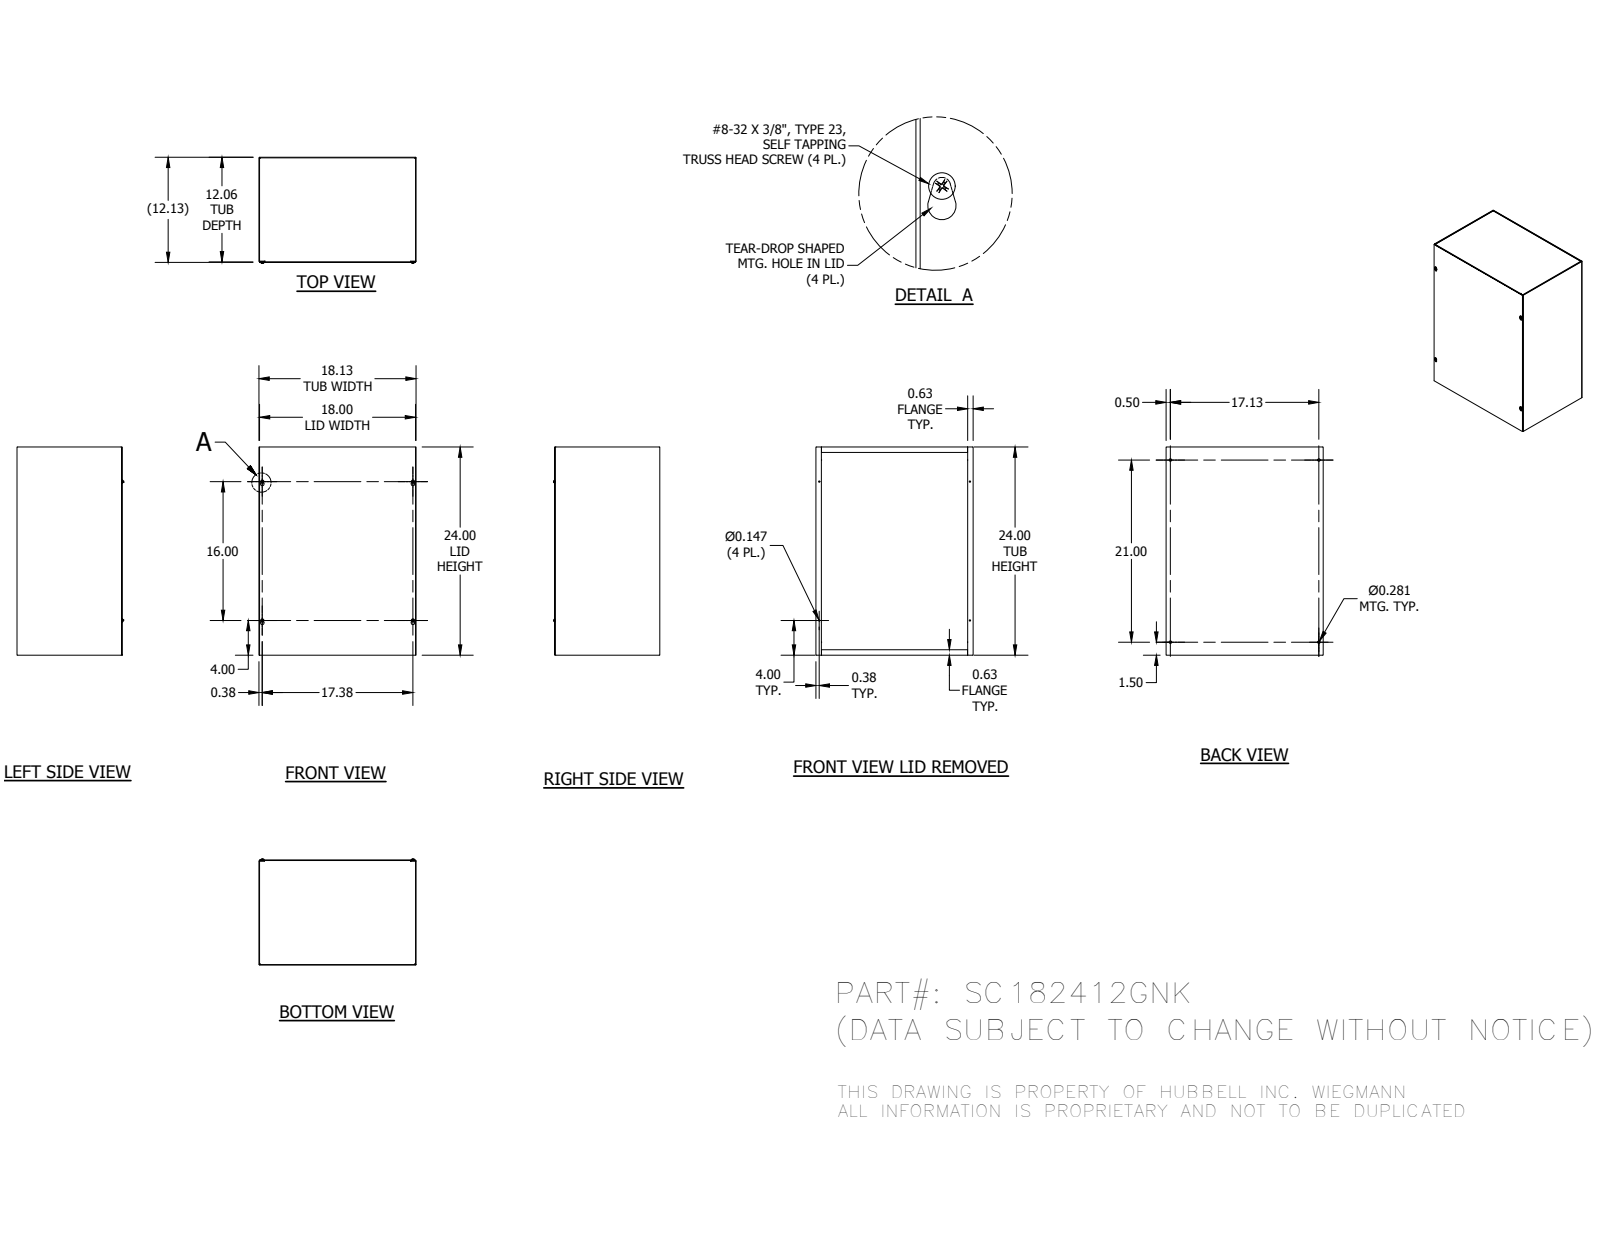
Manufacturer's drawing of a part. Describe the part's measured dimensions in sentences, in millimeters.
The part is named "SC182412GNKBLR; SC1812GNKTB; SC1824GLPA; 34056 (+1 more)". Its 3-D file was written by "Autodesk Inventor 2014 (AUTOMOTIVE_DESIGN)". It is 8 solids with 268 faces: 152 planar, 48 cylindrical and 68 other. Overall it measures 609.6 by 460.38 by 310.52 millimeters. Its volume is 2 011 000 cubic millimeters and its surface area 2 548 000 square millimeters. Round holes: 4 of diameter 3.73, 4 of diameter 7.14. Round bosses or shafts: 4 of diameter 9.75, 4 of diameter 4.17. Partial cylindrical surfaces (rounded edges, fillets, slot ends): 12 of radius 0.4, 12 of radius 1.98, 4 of radius 3.17, 4 of radius 5.16. The main face-to-face distances are 1.59, 306.39, 458.79, 304.8, 307.98, 608.01, 457.2, 460.38, 609.6, 606.42. The hole center spacings are 63.58, 442.73, 469.91, 642.48, 406.4, 434.98, 441.32, 533.4.
